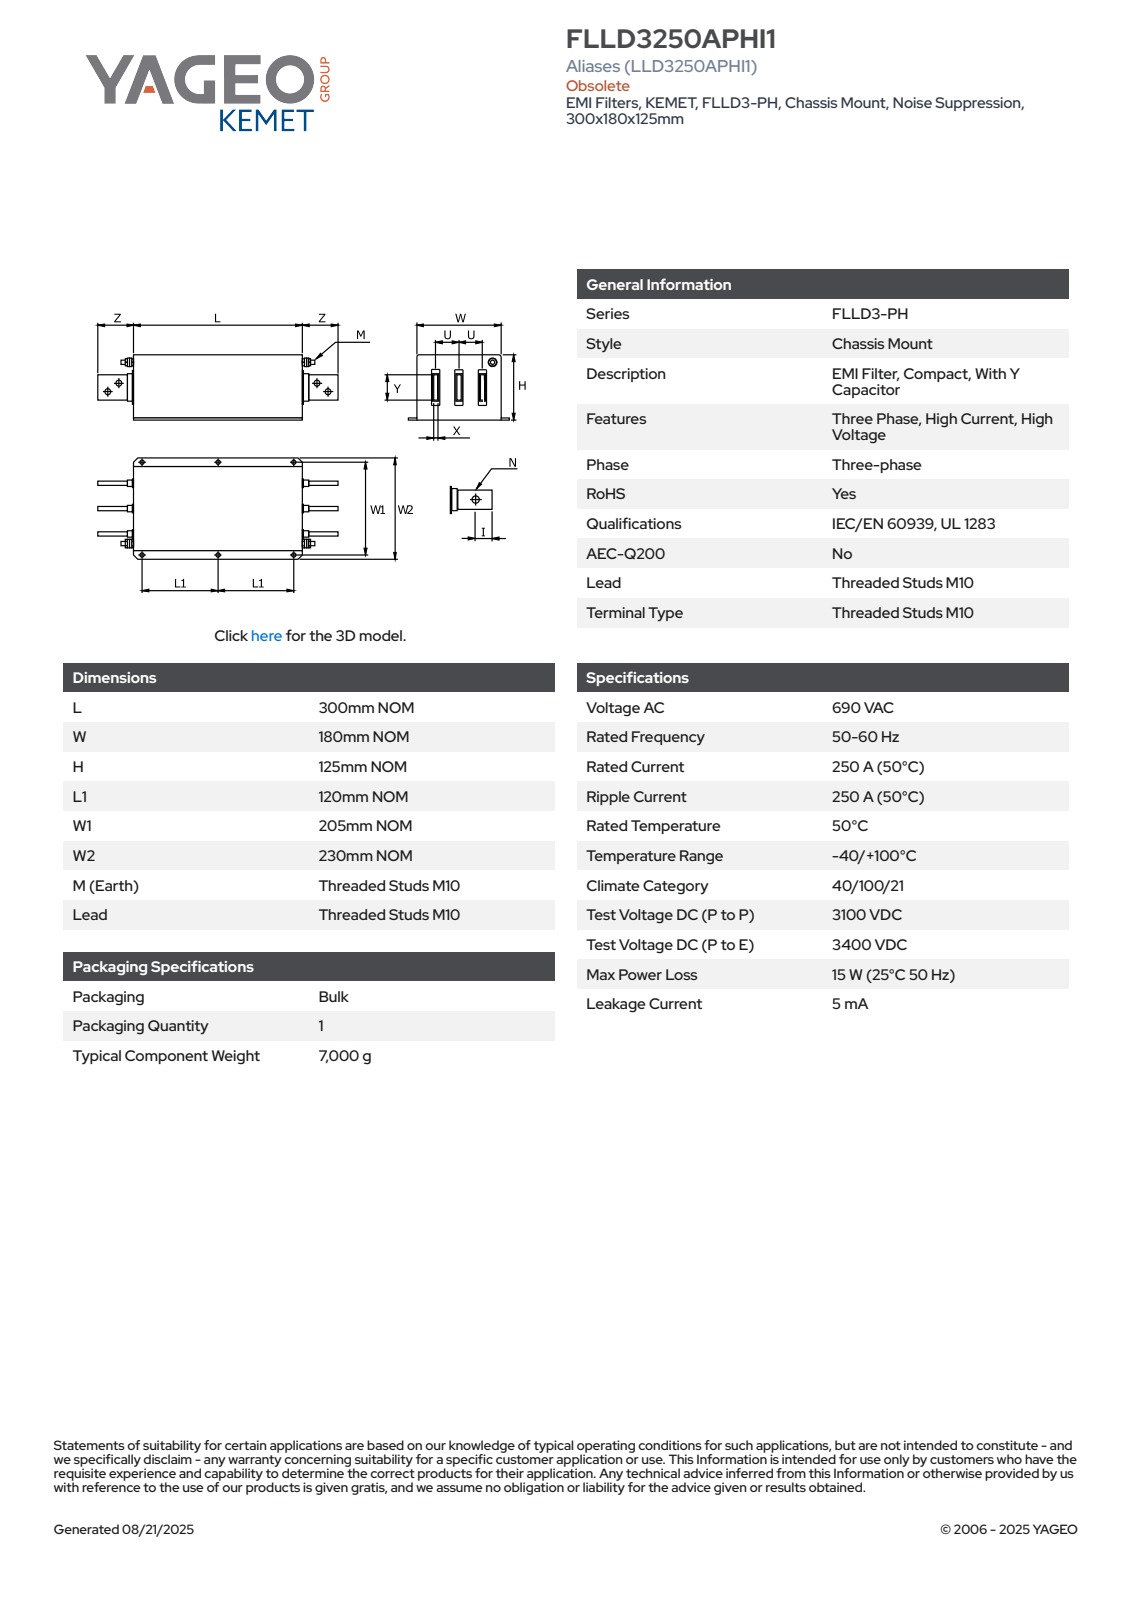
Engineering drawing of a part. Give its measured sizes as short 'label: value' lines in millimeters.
name: HEX NUT M12x1.75_90592A028; 094-00233 Case 250A 300x180x125 RevC; 094-00233 Case 250A utan tank bush RevC; Busbar 5x20^FLLD3250APVI1_EXT (+8 more)
written by: SolidWorks 2021 (AUTOMOTIVE_DESIGN)
unit: mm
bodies: 80 solids, 3010 faces (770 planar, 926 cylindrical, 1314 other)
size: 390 × 230 × 125
volume: 556 351 mm³; area: 624 277 mm²
holes: 19× ⌀1.8, 13× ⌀3.4, 10× ⌀3.2, 6× ⌀12, 4× ⌀5, 4× ⌀5.2, 2× ⌀9, 1× ⌀13, 1× ⌀14
bosses: 13× ⌀3.2, 4× ⌀7, 1× ⌀24, 1× ⌀12
rounds: 60× R2, 48× R0.5, 36× R0.2, 30× R1, 24× R0.25, 10× R2.5, 4× R1.5, 2× R3
face distances: 2, 1, 178, 123, 298, 125, 122, 124, 296, 176
hole spacings: 120, 26.97, 55, 74.33, 76.66, 103.09, 166.33, 237.54
